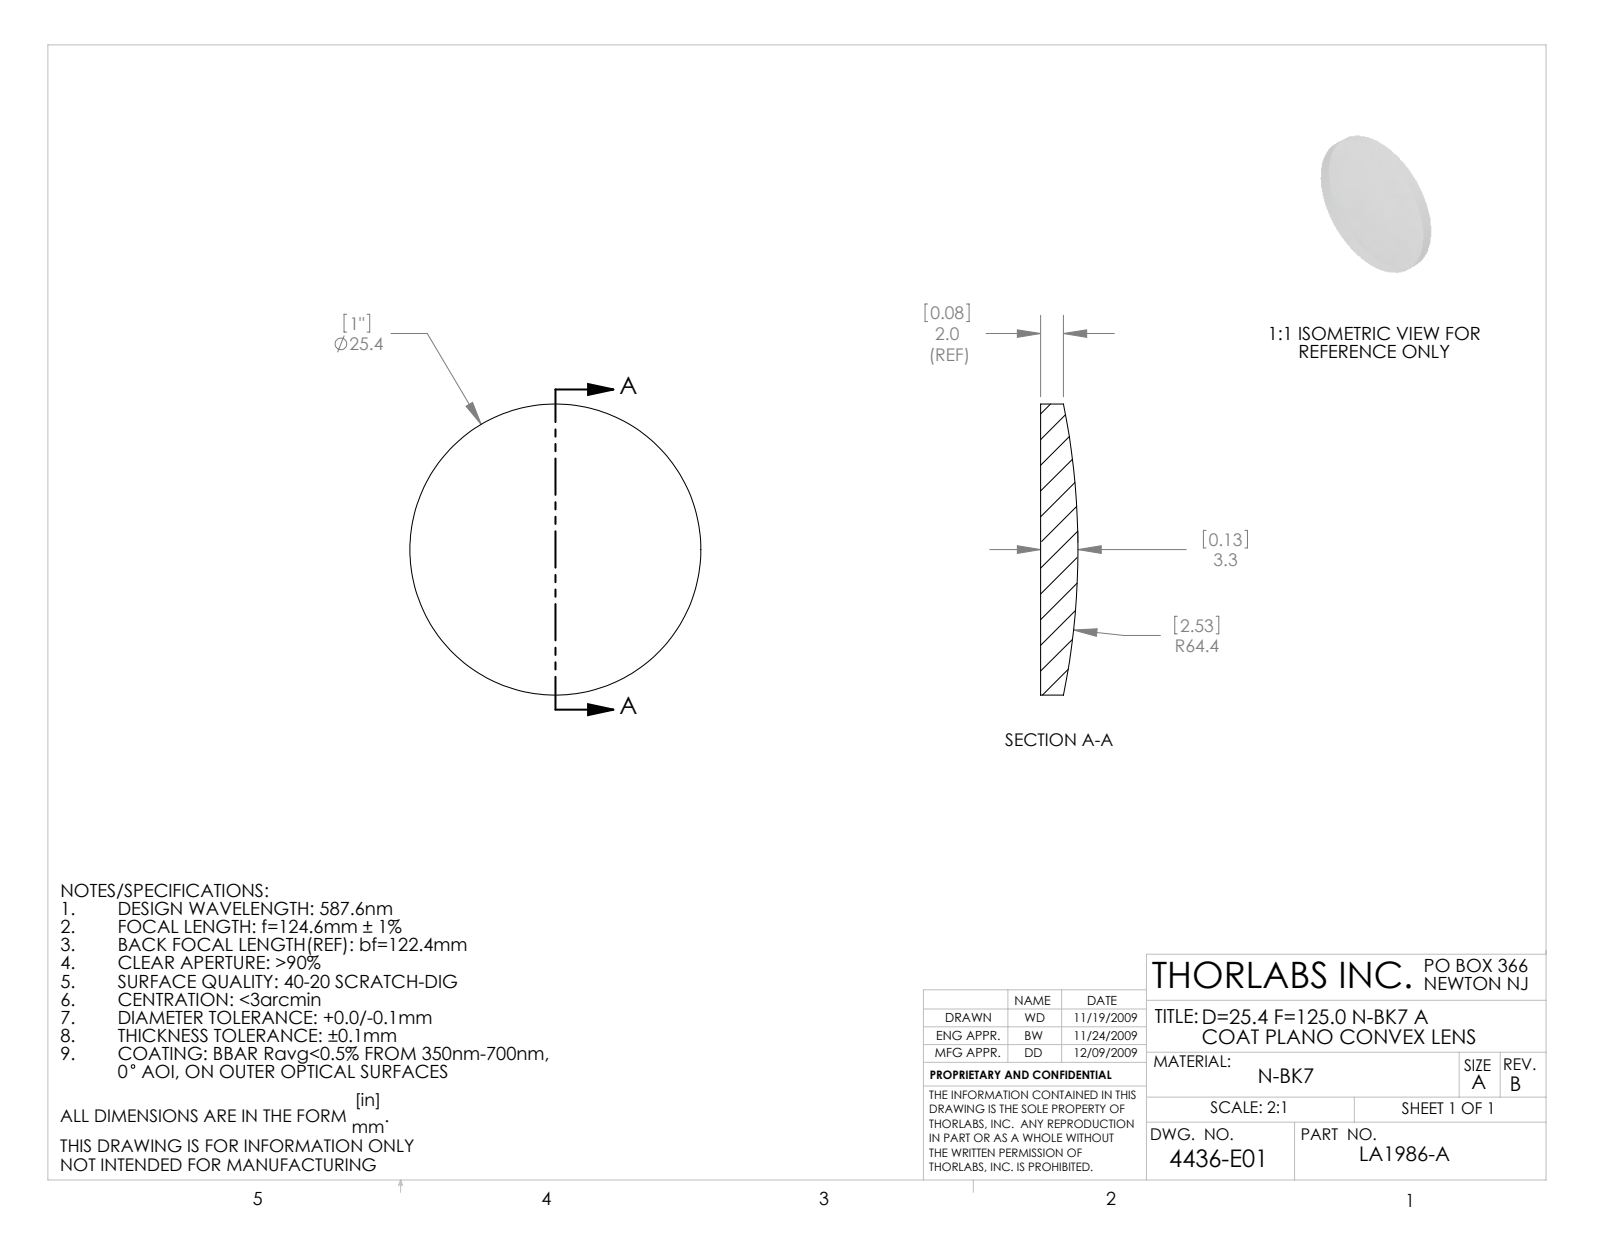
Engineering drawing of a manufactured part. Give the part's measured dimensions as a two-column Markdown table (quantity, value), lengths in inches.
| quantity | value |
| --- | --- |
| part name | 4436-E0W |
| STEP written by | SolidWorks 2009 (AUTOMOTIVE_DESIGN) |
| units | inches |
| bodies | 1 solid, 5 faces (1 planar, 2 cylindrical, 2 other) |
| overall size | 1 × 1 × 0.128 |
| volume | 0.081 in³ |
| surface area | 1.826 in² |
| round bosses / shafts (diameter × count) | 1 × 1 |
